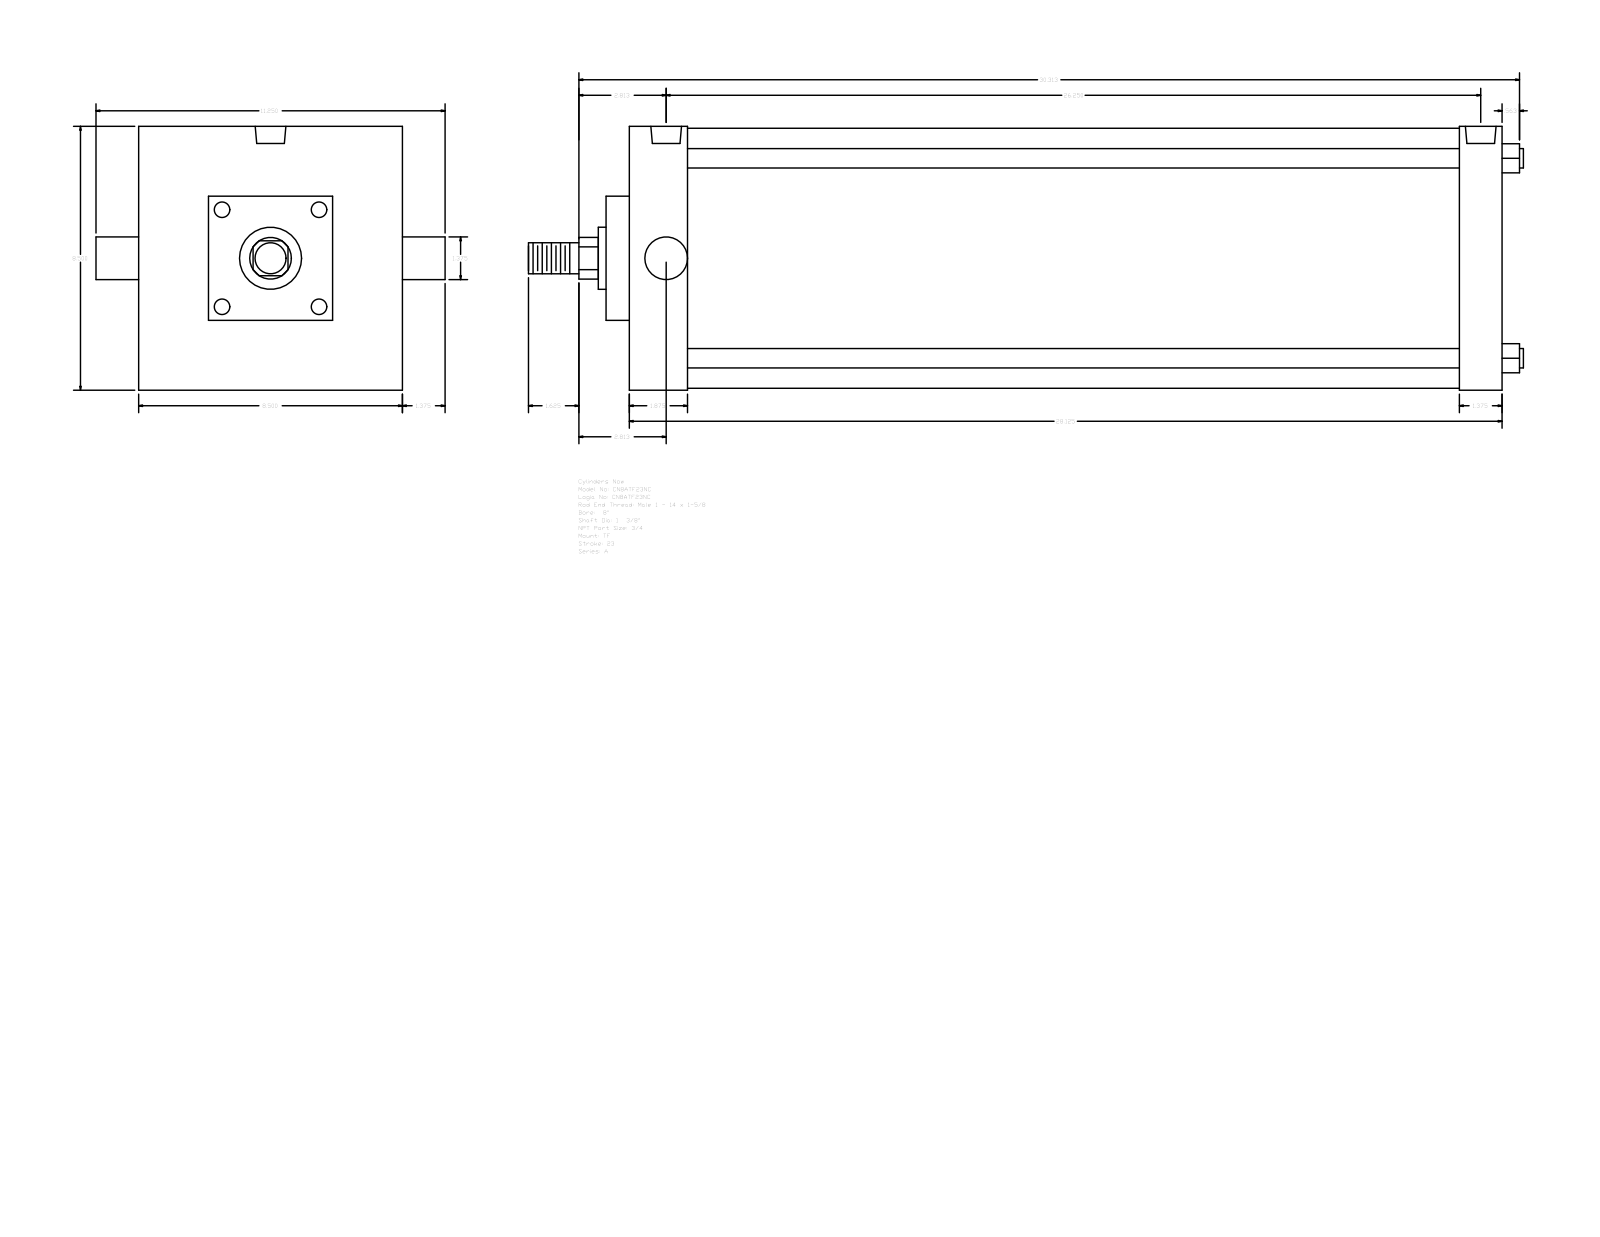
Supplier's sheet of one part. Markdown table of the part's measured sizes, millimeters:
| quantity | value |
| --- | --- |
| part name | A_TF__0800_1.375 |
| STEP written by | GSSL Pune (CONFIG_CONTROL_DESIGN) |
| units | millimeters |
| bodies | 0 solids, 89 faces (65 planar, 24 cylindrical, 0 other) |
| overall size | 814.39 × 285.75 × 215.9 |
| round holes (diameter × count) | 15.08 × 3, 25.12 × 2 |
| round bosses / shafts (diameter × count) | 15.88 × 4, 34.92 × 2, 212.72 × 1, 50.8 × 1, 25.4 × 1 |
| partial cylindrical surfaces (radius × count) | 17.06 × 1 |
| main face-to-face distances | 714.38, 215.9, 47.63, 666.75, 679.46, 631.83, 34.92, 19.04, 66.67, 698.5 |
| hole center spacings | 6.35, 660.4, 654.05, 666.75 |
